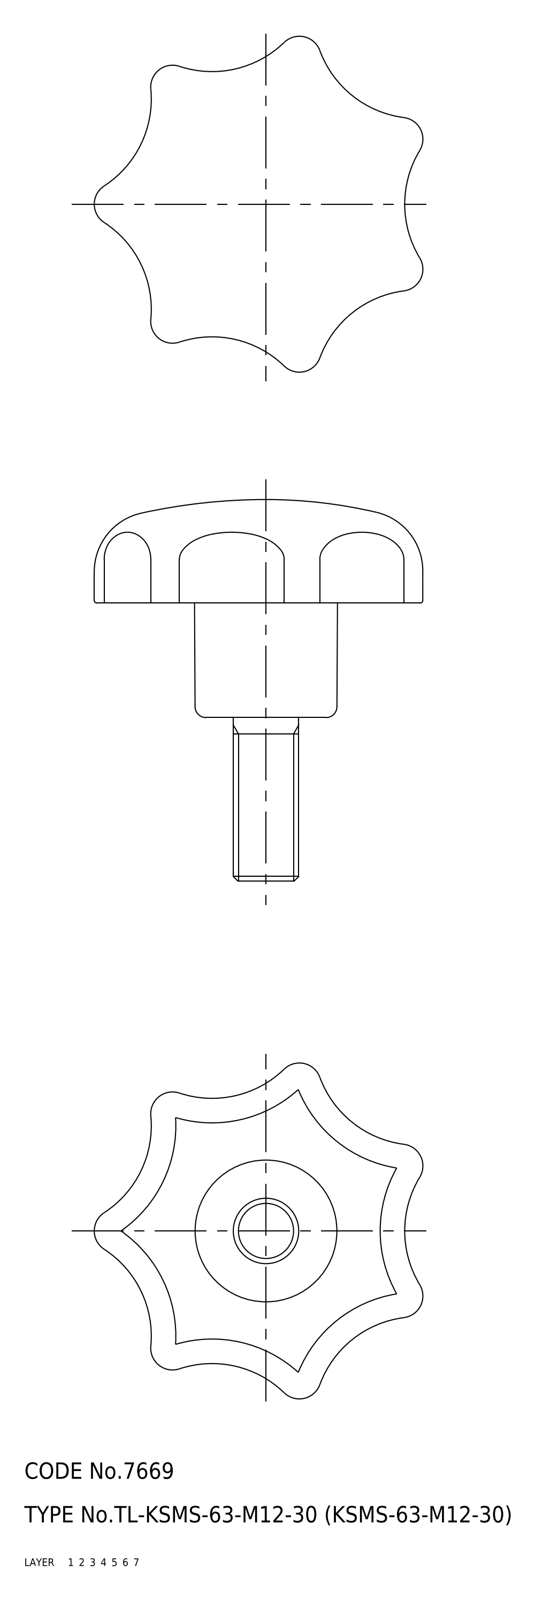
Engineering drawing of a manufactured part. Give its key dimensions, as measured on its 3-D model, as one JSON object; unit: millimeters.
{"part_name": "screw; knob; KSMS_63_M12_30_10377_36", "step_written_by": "CADfix (AUTOMOTIVE_DESIGN)", "units": "millimeters", "bodies": {"solids": 2, "faces": 100, "planar": 0, "cylindrical": 0, "other": 100}, "overall_size": [70, 61.62, 60.28], "volume_mm3": 39633, "surface_area_mm2": 15905}
